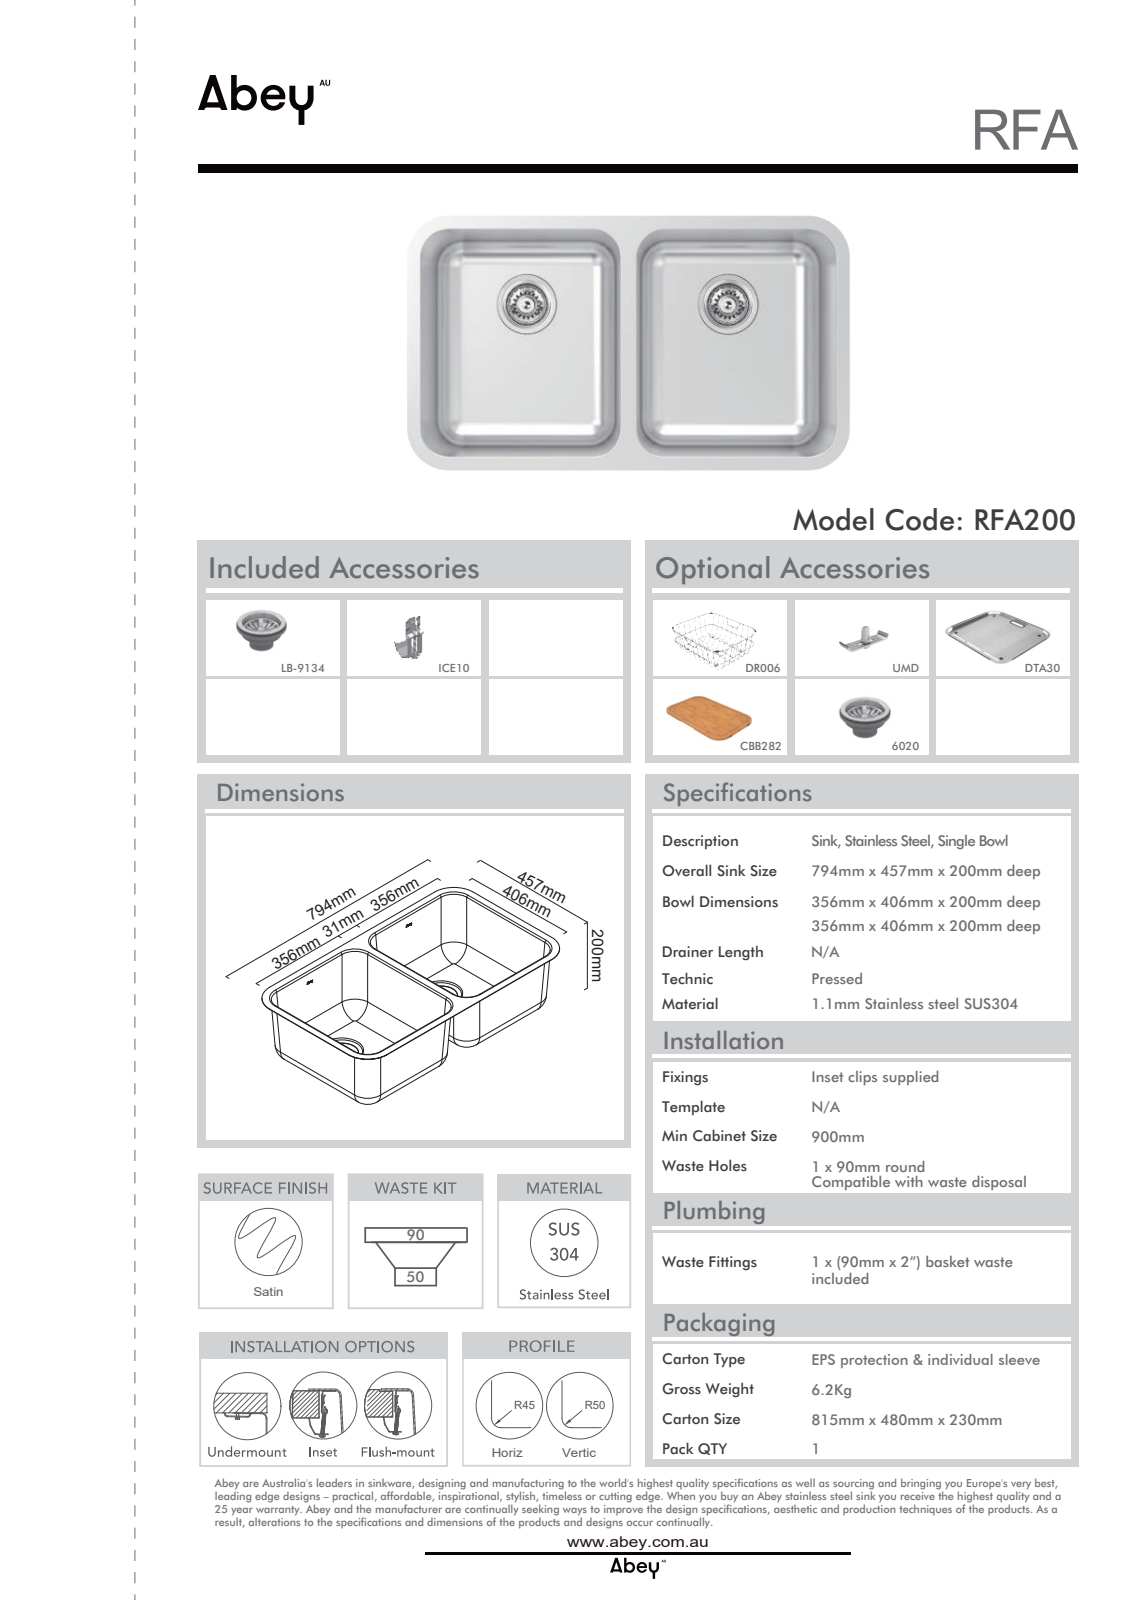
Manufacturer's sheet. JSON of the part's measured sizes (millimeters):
{"part_name": "RFA200", "step_written_by": "SolidWorks 2022 (CONFIG_CONTROL_DESIGN)", "units": "millimeters", "bodies": {"solids": 1, "faces": 134, "planar": 22, "cylindrical": 56, "other": 56}, "overall_size": [794, 457, 210.02], "volume_mm3": 805069, "surface_area_mm2": 1651000, "round_holes": [[91.1, 2]], "partial_cylinders_radius": [[50, 8], [51, 8], [4, 6], [5, 6], [45, 6], [46, 6], [75, 4]], "face_to_face_distances": [1, 386.61, 387.61, 385.61, 457, 794], "hole_center_spacings": [387]}
